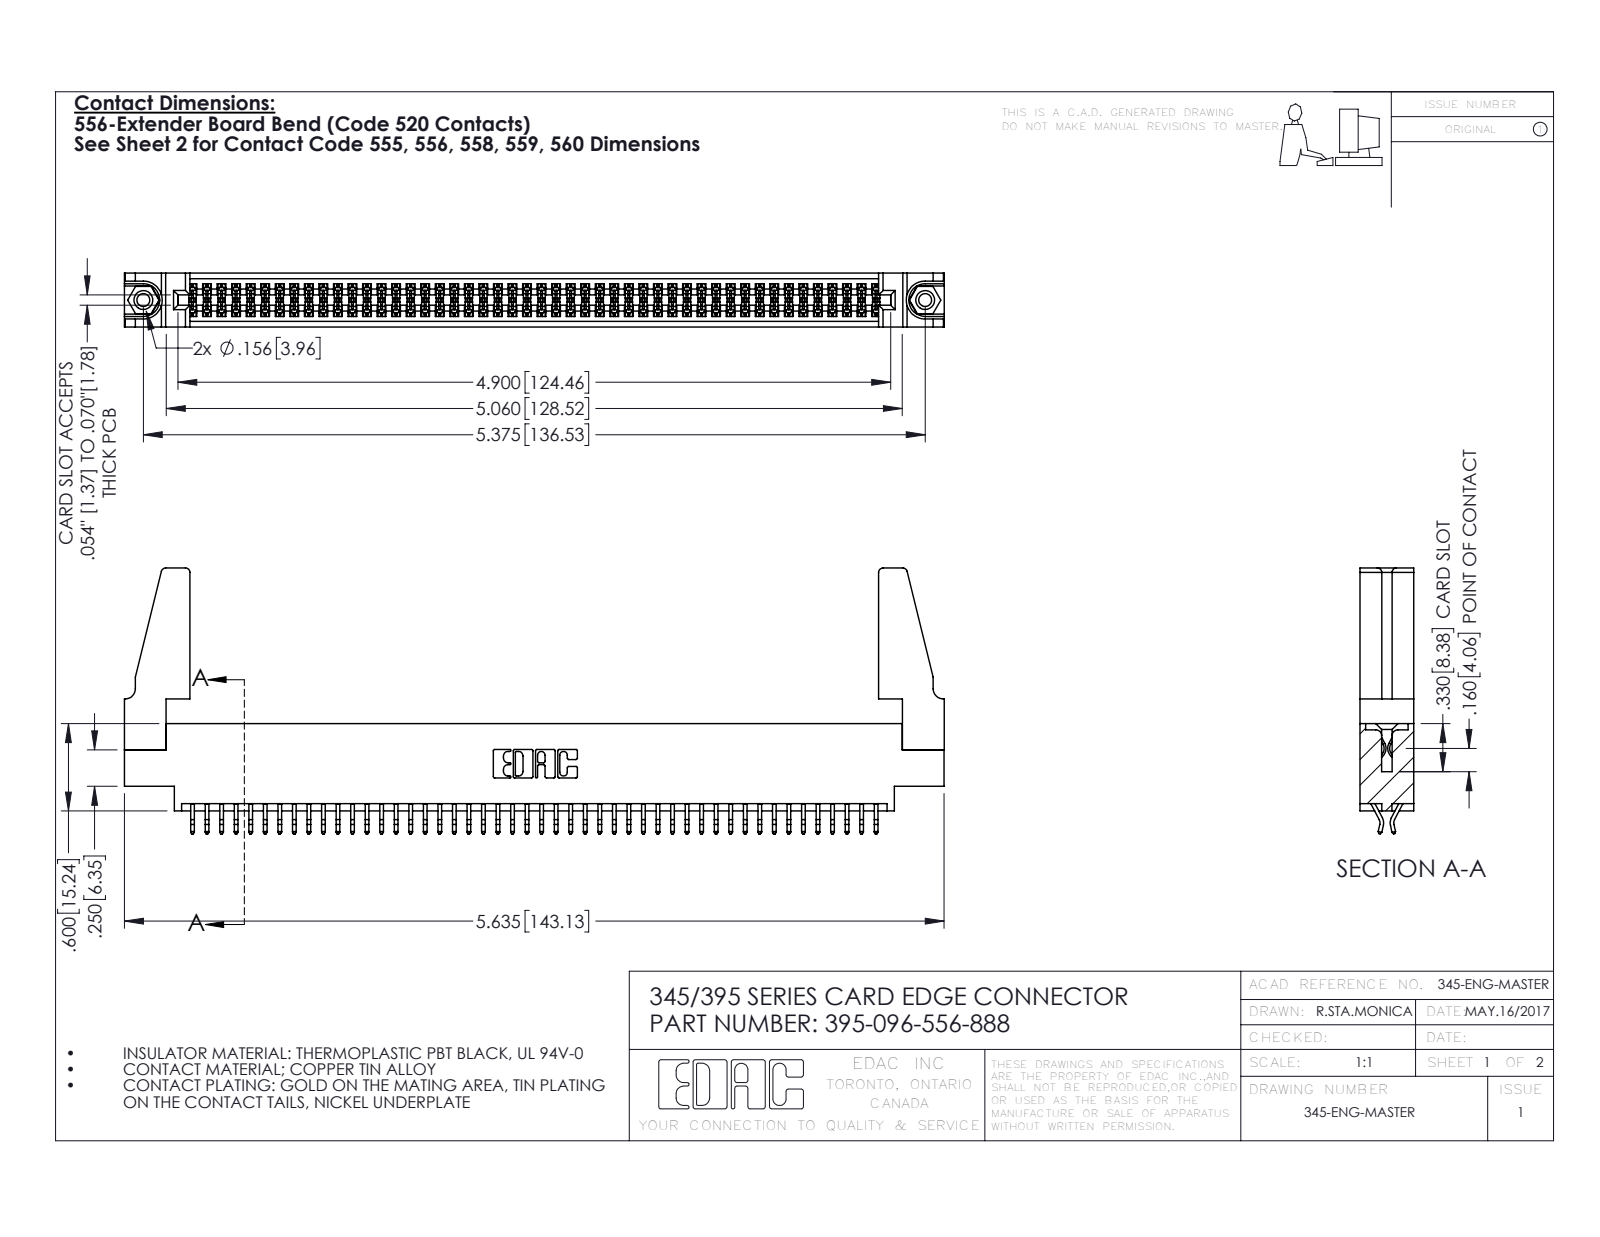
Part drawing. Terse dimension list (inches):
name: 395-096-556-888; 345-292-001_556 Tail; 345 Part_0.170 Offset - 0.156 Dia-TH; 345-220-078_345-220-088 (+1 more)
written by: SolidWorks 2016 (CONFIG_CONTROL_DESIGN)
unit: in
bodies: 101 solids, 5630 faces (3708 planar, 1906 cylindrical, 16 other)
size: 5.636 × 1.827 × 0.37
volume: 1.043 in³; area: 36.83 in²
holes: 2× ⌀0.089, 2× ⌀0.125, 2× ⌀0.156, 1× ⌀0.064
bosses: 2× ⌀0.155
rounds: 144× R0.006, 22× R0.01, 8× R0.03, 6× R0.007, 6× R0.031, 3× R0.026, 2× R0.01, 2× R0.014
face distances: 0.072, 0.298, 0.37, 0.025, 0.098, 0.272, 0.2, 0.225, 0.175, 0.149
hole spacings: 0.27, 5.139, 5.375
